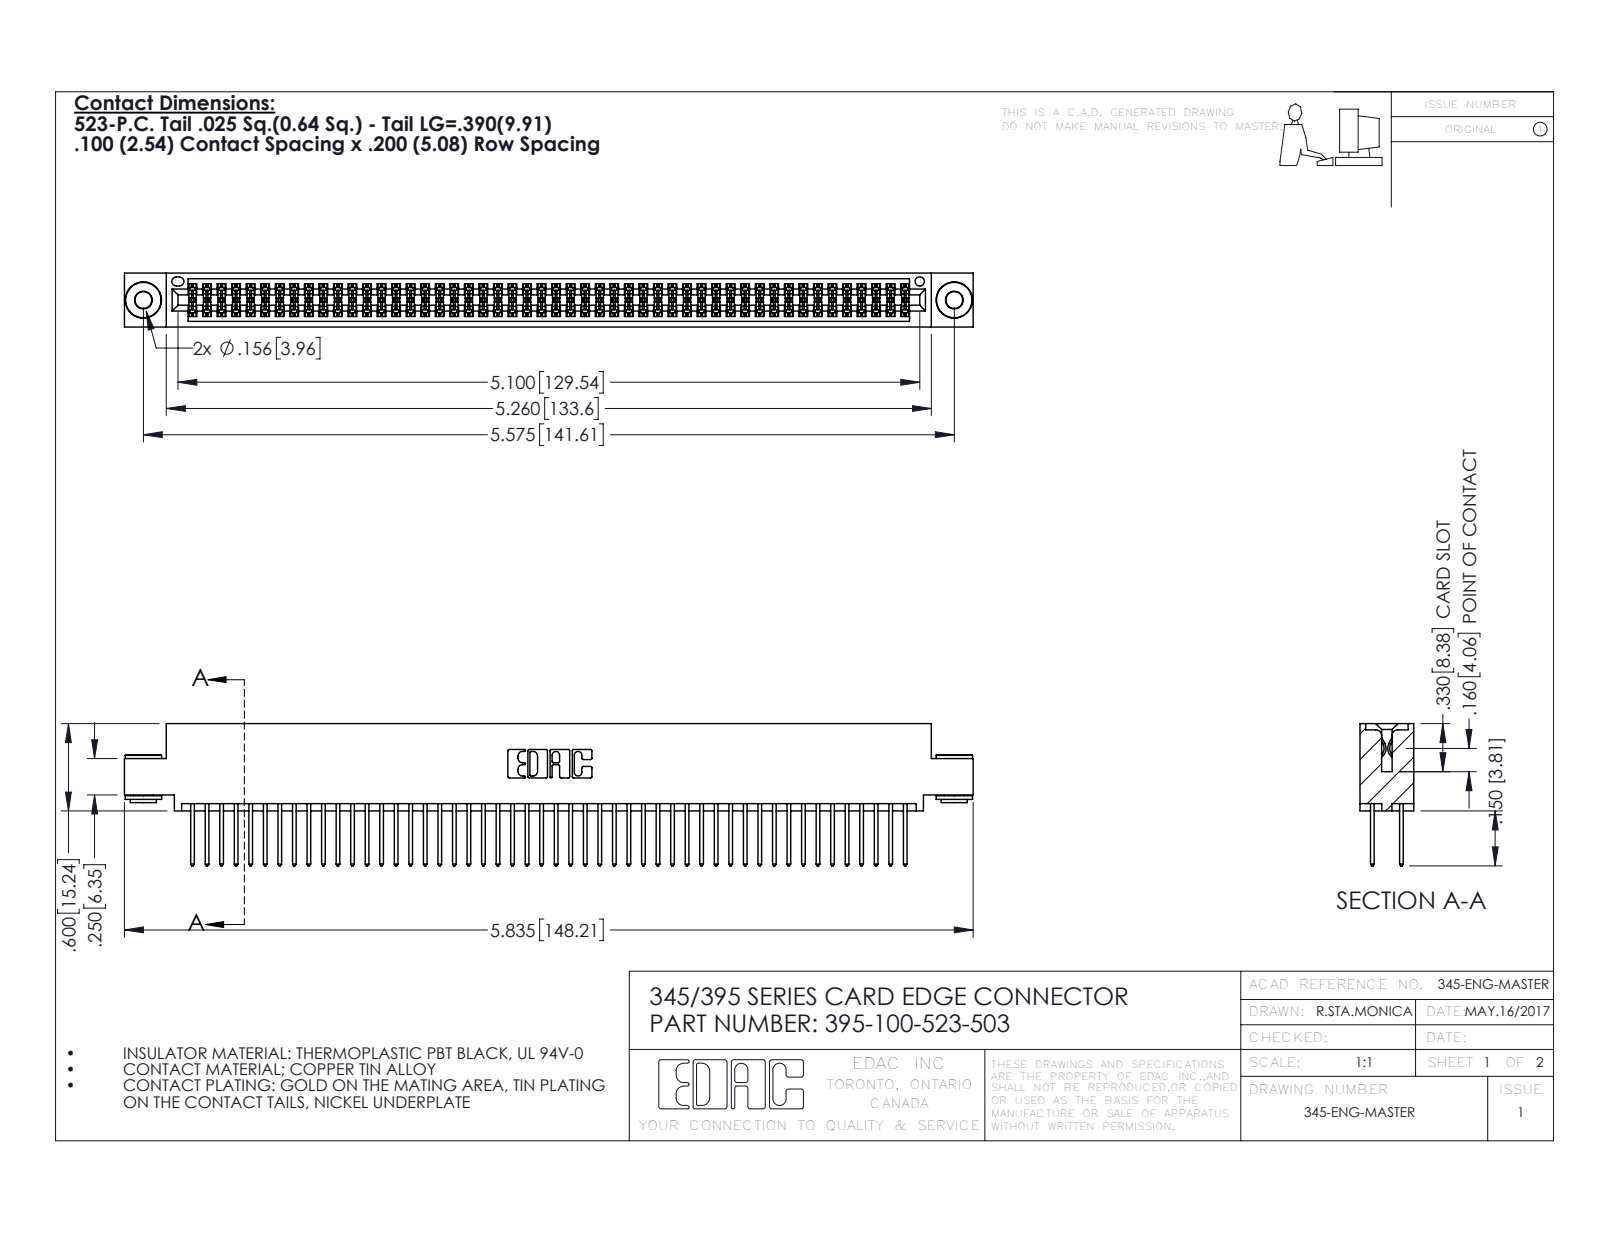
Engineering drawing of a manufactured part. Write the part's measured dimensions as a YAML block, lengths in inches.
part_name: "345-250-002_345-250-002-102; 395-100-523-503; 345 Part_0.110 Offset - 0.156 Dia-TH; 345-292-001_345-293-123"
step_written_by: "SolidWorks 2016 (CONFIG_CONTROL_DESIGN)"
units: inches
bodies: {solids: 103, faces: 5168, planar: 3394, cylindrical: 1766, other: 8}
overall_size: [5.835, 0.977, 0.37]
volume: 0.892
surface_area: 35.63
round_holes:
  - {diameter: 0.116, count: 2}
  - {diameter: 0.156, count: 2}
  - {diameter: 0.064, count: 1}
round_bosses_or_shafts:
  - {diameter: 0.25, count: 2}
  - {diameter: 0.18, count: 2}
  - {diameter: 0.136, count: 2}
partial_cylinders:
  - {radius: 0.006, count: 150}
  - {radius: 0.01, count: 100}
  - {radius: 0.01, count: 22}
  - {radius: 0.007, count: 6}
  - {radius: 0.031, count: 6}
  - {radius: 0.026, count: 3}
  - {radius: 0.014, count: 2}
  - {radius: 0.019, count: 2}
face_to_face_distances: [0.072, 0.298, 0.2, 0.025, 0.098, 0.272, 0.37, 0.225, 0.175, 0.149]
hole_center_spacings: [0.27, 5.339, 5.575]
